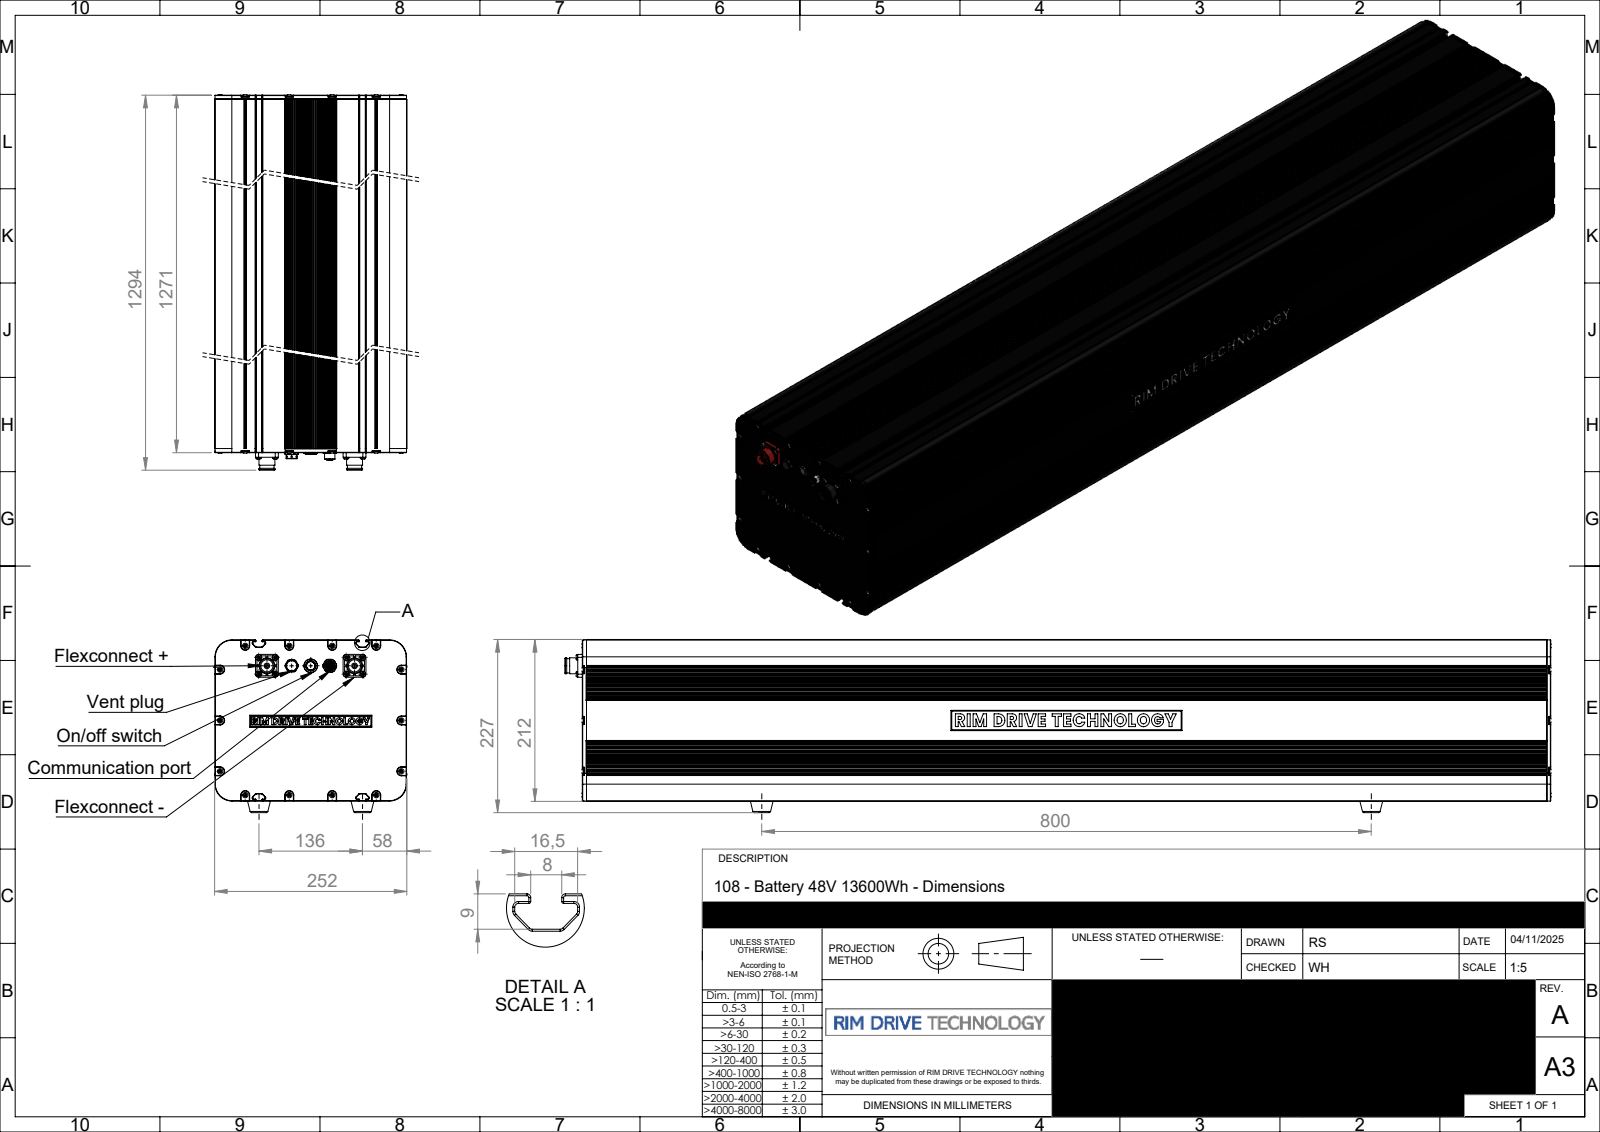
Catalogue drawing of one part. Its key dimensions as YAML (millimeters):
part_name: "P-108-201-rev-A-48V 13600Wh"
step_written_by: "SolidWorks 2024 (AUTOMOTIVE_DESIGN)"
units: millimeters
bodies: {solids: 1, faces: 4104, planar: 1829, cylindrical: 1340, other: 935}
overall_size: [1294.6, 252.36, 227.1]
volume: 66200000
surface_area: 1563000
round_holes:
  - {diameter: 1.1, count: 4}
  - {diameter: 10.6, count: 4}
  - {diameter: 2, count: 3}
  - {diameter: 16, count: 2}
  - {diameter: 7.3, count: 1}
  - {diameter: 11.47, count: 1}
  - {diameter: 11.8, count: 1}
round_bosses_or_shafts:
  - {diameter: 7, count: 22}
  - {diameter: 9.5, count: 4}
  - {diameter: 21, count: 2}
  - {diameter: 18.6, count: 2}
  - {diameter: 7.5, count: 2}
  - {diameter: 17.8, count: 1}
  - {diameter: 14.5, count: 1}
  - {diameter: 13.57, count: 1}
partial_cylinders:
  - {radius: 0.5, count: 292}
  - {radius: 0.34, count: 84}
  - {radius: 0.59, count: 84}
  - {radius: 0.29, count: 48}
  - {radius: 0.69, count: 48}
  - {radius: 1, count: 32}
  - {radius: 0.45, count: 24}
  - {radius: 0.79, count: 24}
face_to_face_distances: [211.4, 251.36, 0.5, 250.86, 2.5, 208.9, 1271, 5, 250.36, 206.4]
hole_center_spacings: [2.33, 3.3, 4.67, 23.41, 25, 26.7, 30.89, 32.5]
